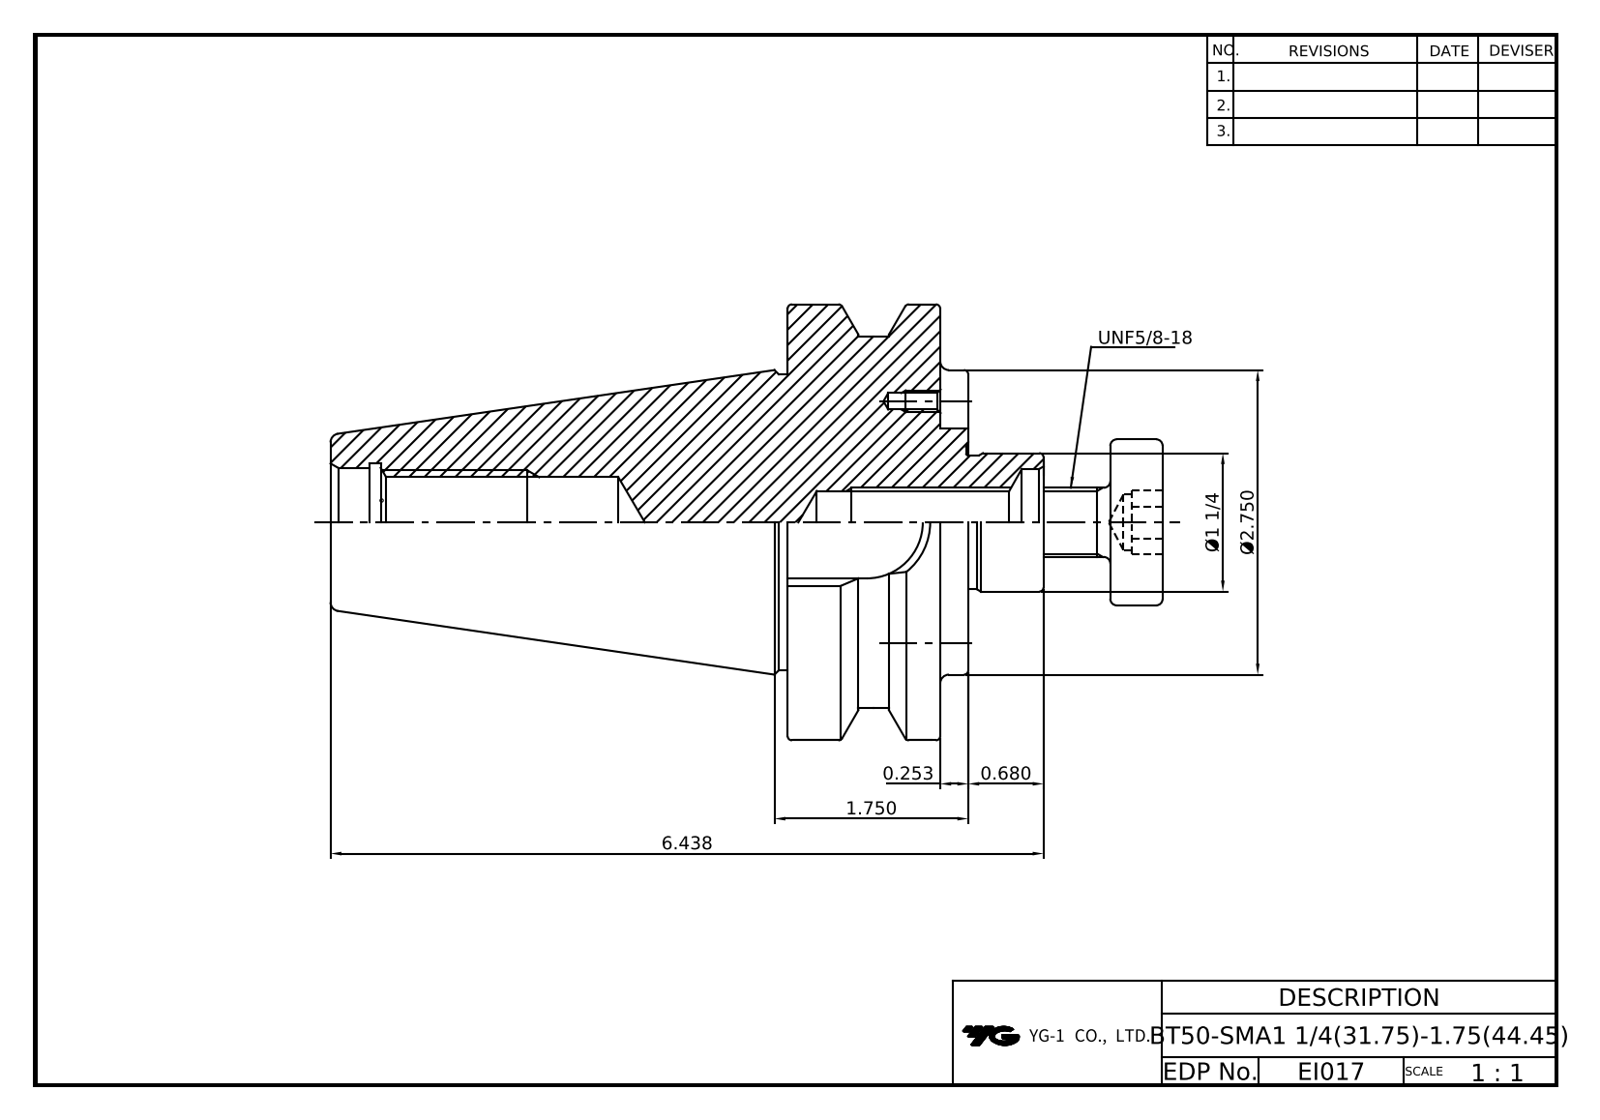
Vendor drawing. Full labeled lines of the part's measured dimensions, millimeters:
Part name (STEP PRODUCT): LO-BT50-SMA31.75-44.45; DRIVE KEY-12.7x12.7x12.7; HEX'' WRENCH BOLT-UNC#10-24x1_2L; COLLAR BOLT-UNF5_8-18x40L
STEP written by: Autodesk Inventor 2026 (AUTOMOTIVE_DESIGN)
Units: millimetres
Bodies: 6 solids, 129 faces (68 planar, 32 cylindrical, 29 other)
Overall size (bounding box): 190.5 × 100 × 100
Volume: 505 400 mm³ · Surface area: 67 030 mm²
Round holes (diameter × count): ⌀3.7 ×2, ⌀5.5 ×2, ⌀8.7 ×2, ⌀12.7 ×1, ⌀14.4 ×1, ⌀20.8 ×1, ⌀24.5 ×1, ⌀25 ×1, ⌀25.6 ×1
Round bosses / shafts (diameter × count): ⌀7.9 ×2, ⌀4.8 ×2, ⌀100 ×1, ⌀84.6 ×1, ⌀69.9 ×1, ⌀69.3 ×1, ⌀38.1 ×1, ⌀31.8 ×1
Partial cylindrical surfaces — rounded edges, fillets, slot ends (radius × count): R6.4 ×2, R12.9 ×1
Main face-to-face distances: 35, 41.5, 6.5, 85.7, 50.7, 44.3, 73.7, 38.7, 32.3, 12
Hole centre spacings: 27.8, 27.8, 55.5, 55.5, 55.5
